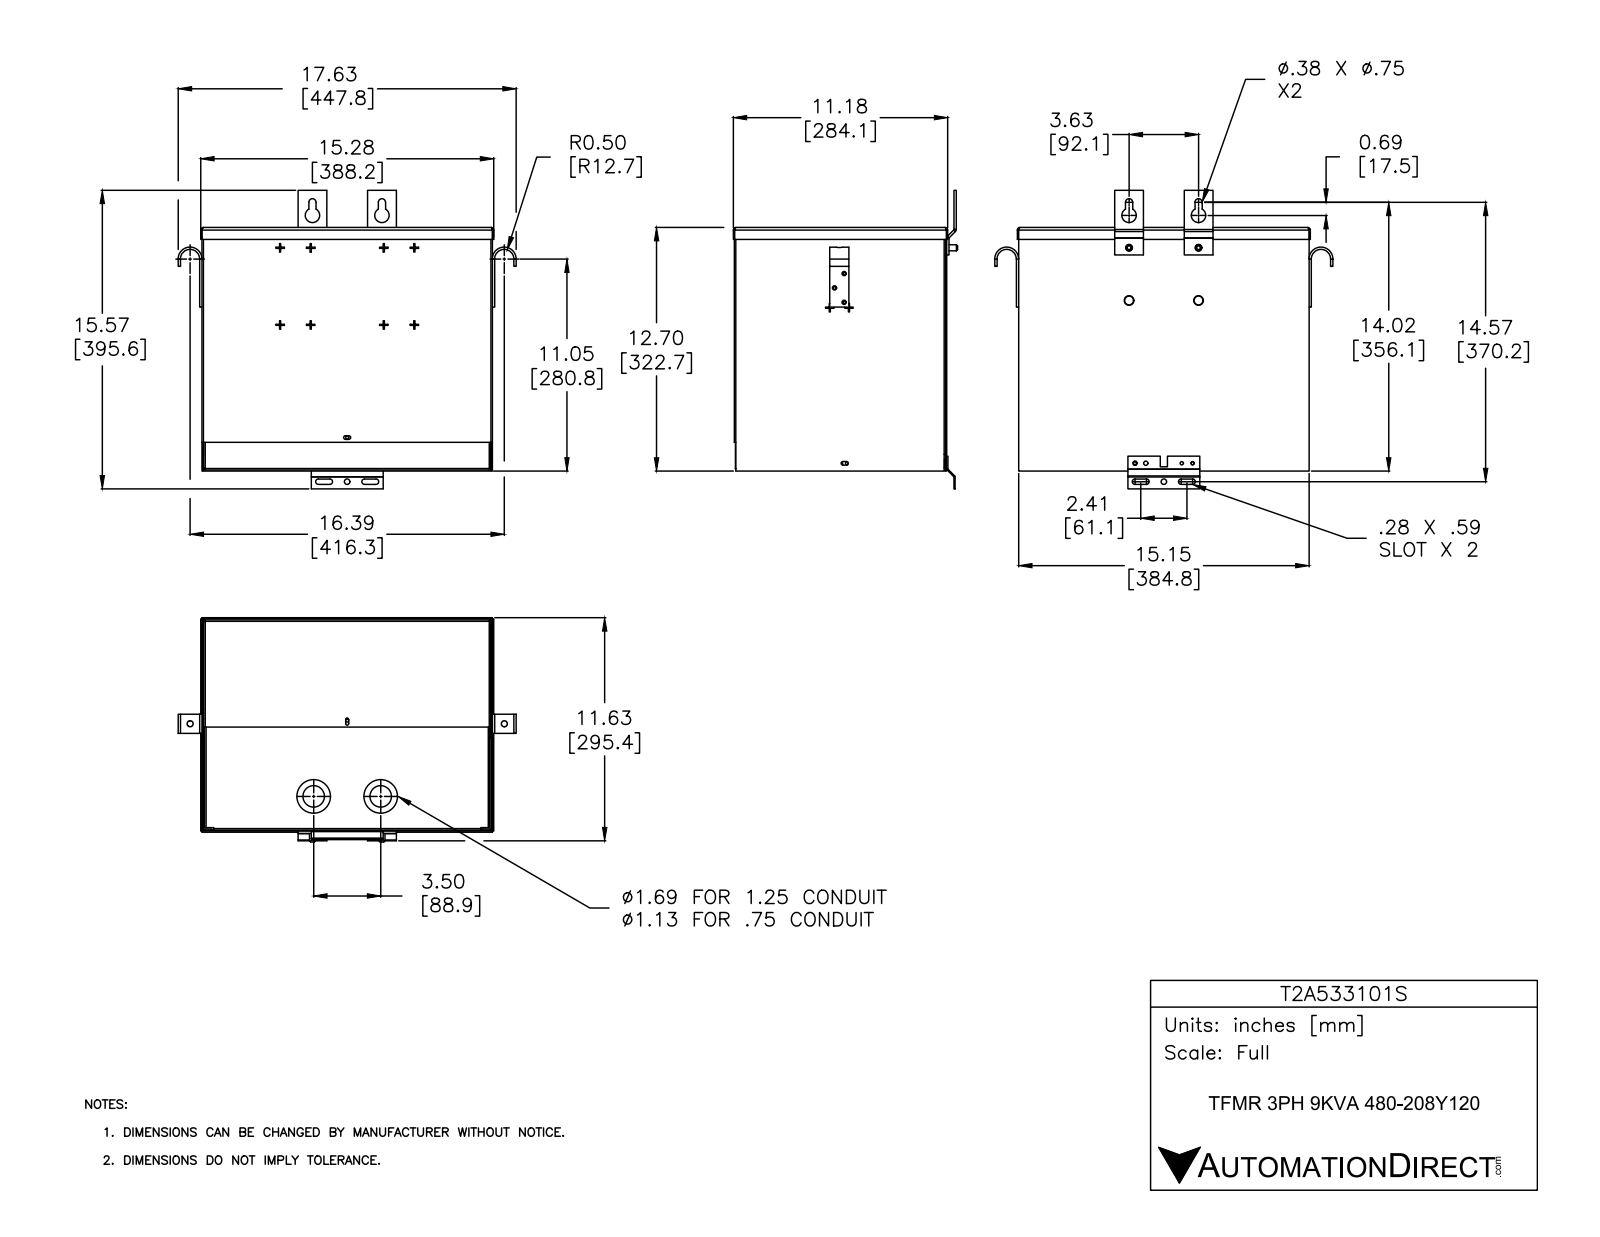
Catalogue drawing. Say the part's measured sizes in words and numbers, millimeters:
The part is named "T2A533101S". Its 3-D file was written by "SolidWorks 2015 (AUTOMOTIVE_DESIGN)". It is 12 solids with 707 faces: 499 planar, 138 cylindrical and 70 other. Overall it measures 447.8 by 395.6 by 297.1 millimeters. Its volume is 1 085 000 cubic millimeters and its surface area 1 421 000 square millimeters. Round holes: 5 of diameter 4.1, 4 of diameter 8, 2 of diameter 4.4, 2 of diameter 5.6, 2 of diameter 7.1, 2 of diameter 8.7, 2 of diameter 19.1, 2 of diameter 28.6, 2 of diameter 44.5, 1 of diameter 4.4, 1 of diameter 4.7. Round bosses or shafts: 2 of diameter 46, 2 of diameter 30.1, 2 of diameter 7.9. Partial cylindrical surfaces (rounded edges, fillets, slot ends): 12 of radius 0.4, 12 of radius 1.9, 8 of radius 2.4, 4 of radius 1.9, 4 of radius 3.4, 4 of radius 3.6, 2 of radius 0.5, 2 of radius 0.8. The main face-to-face distances are 1.5, 279.9, 383.3, 278.4, 281.4, 318, 319.7, 1.7, 384.8, 381.8. The hole center spacings are 14.3, 34.1, 41.6, 42.9, 45.2, 51.2, 61.9, 92.1.
